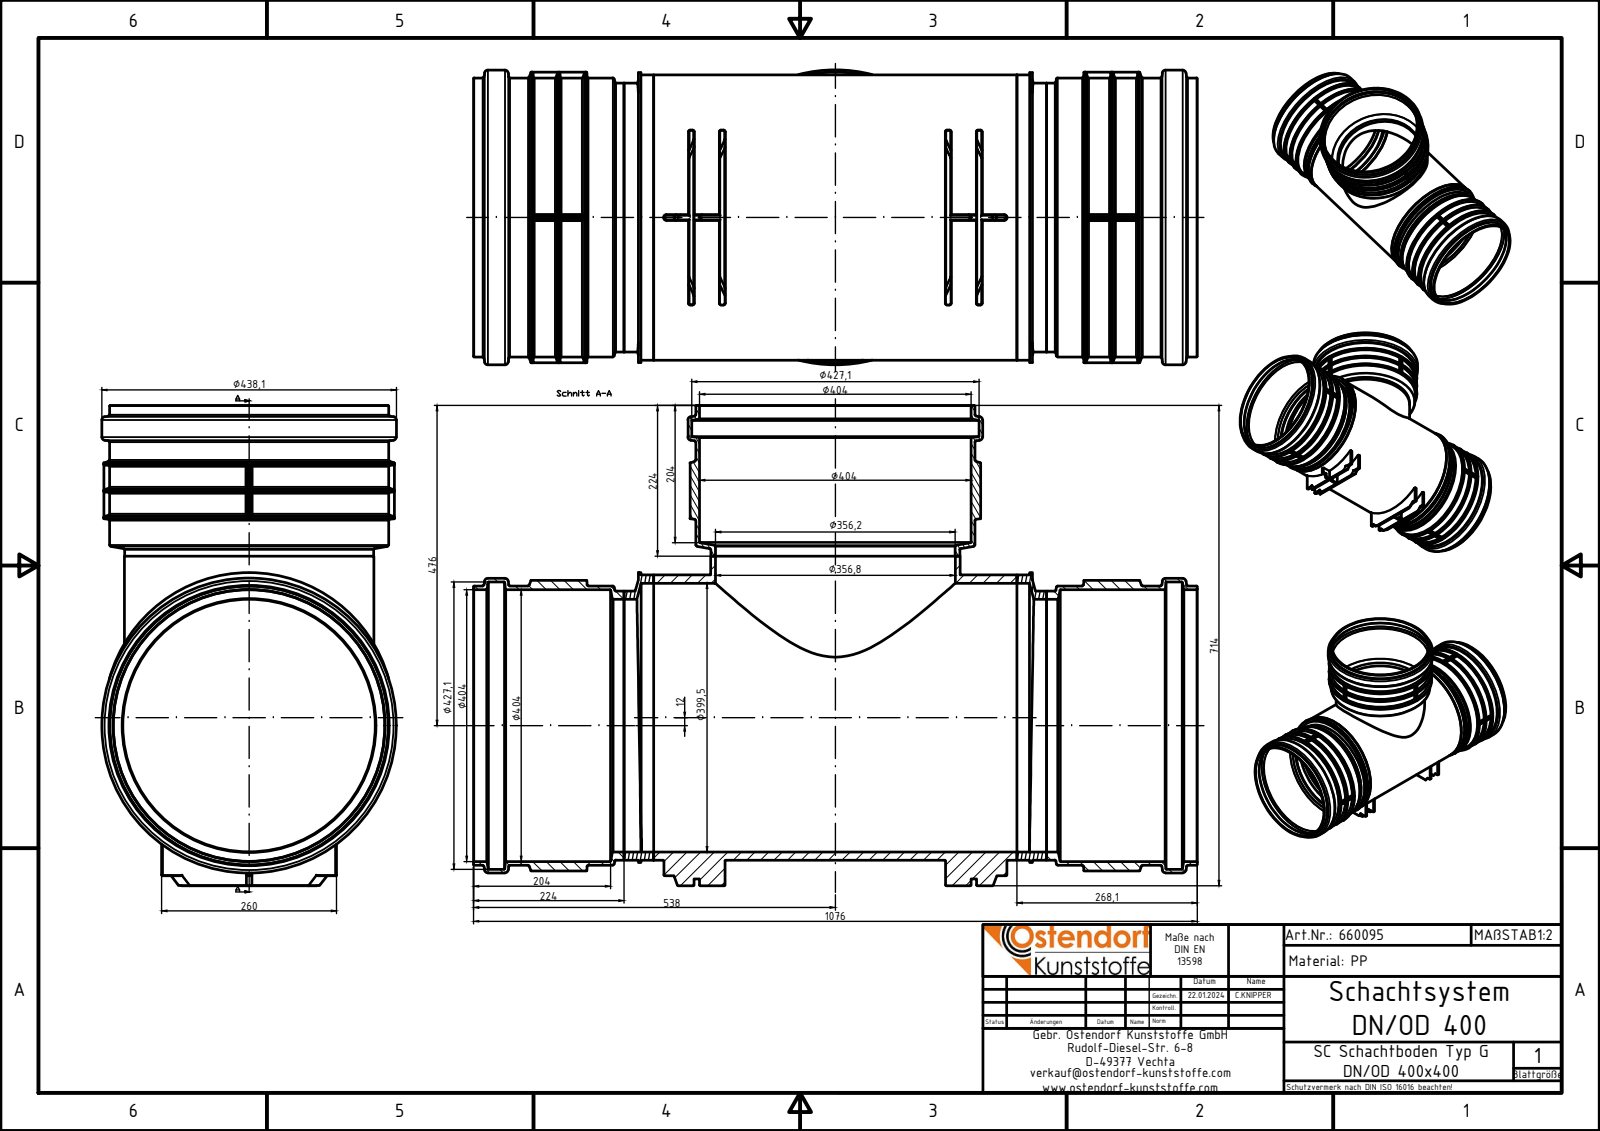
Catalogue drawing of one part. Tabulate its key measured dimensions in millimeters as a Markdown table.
| quantity | value |
| --- | --- |
| part name | 660095z; 660095 Teil 2; 660095 Teil 1; 660095 Teil 3 (+1 more) |
| STEP written by | Autodesk Inventor 2024 (AUTOMOTIVE_DESIGN) |
| units | millimeters |
| bodies | 6 solids, 620 faces (153 planar, 181 cylindrical, 286 other) |
| overall size | 1076.2 × 714 × 438.1 |
| volume | 16 030 000 mm³ |
| surface area | 4 026 000 mm² |
| round holes (diameter × count) | 404 × 2, 427.1 × 2, 356.2 × 1, 356.8 × 1, 375.4 × 1, 399.4 × 1, 399.5 × 1 |
| round bosses / shafts (diameter × count) | 438.1 × 2, 432 × 2, 415 × 2, 431 × 1, 424.1 × 1, 424 × 1, 400 × 1, 371 × 1 |
| partial cylindrical surfaces (radius × count) | 1 × 36, 2 × 24, 4 × 4 |
| main face-to-face distances | 44.1, 584.1, 8, 46, 382, 540, 628.2, 434, 150.1, 478.1 |
| hole center spacings | 12 |
